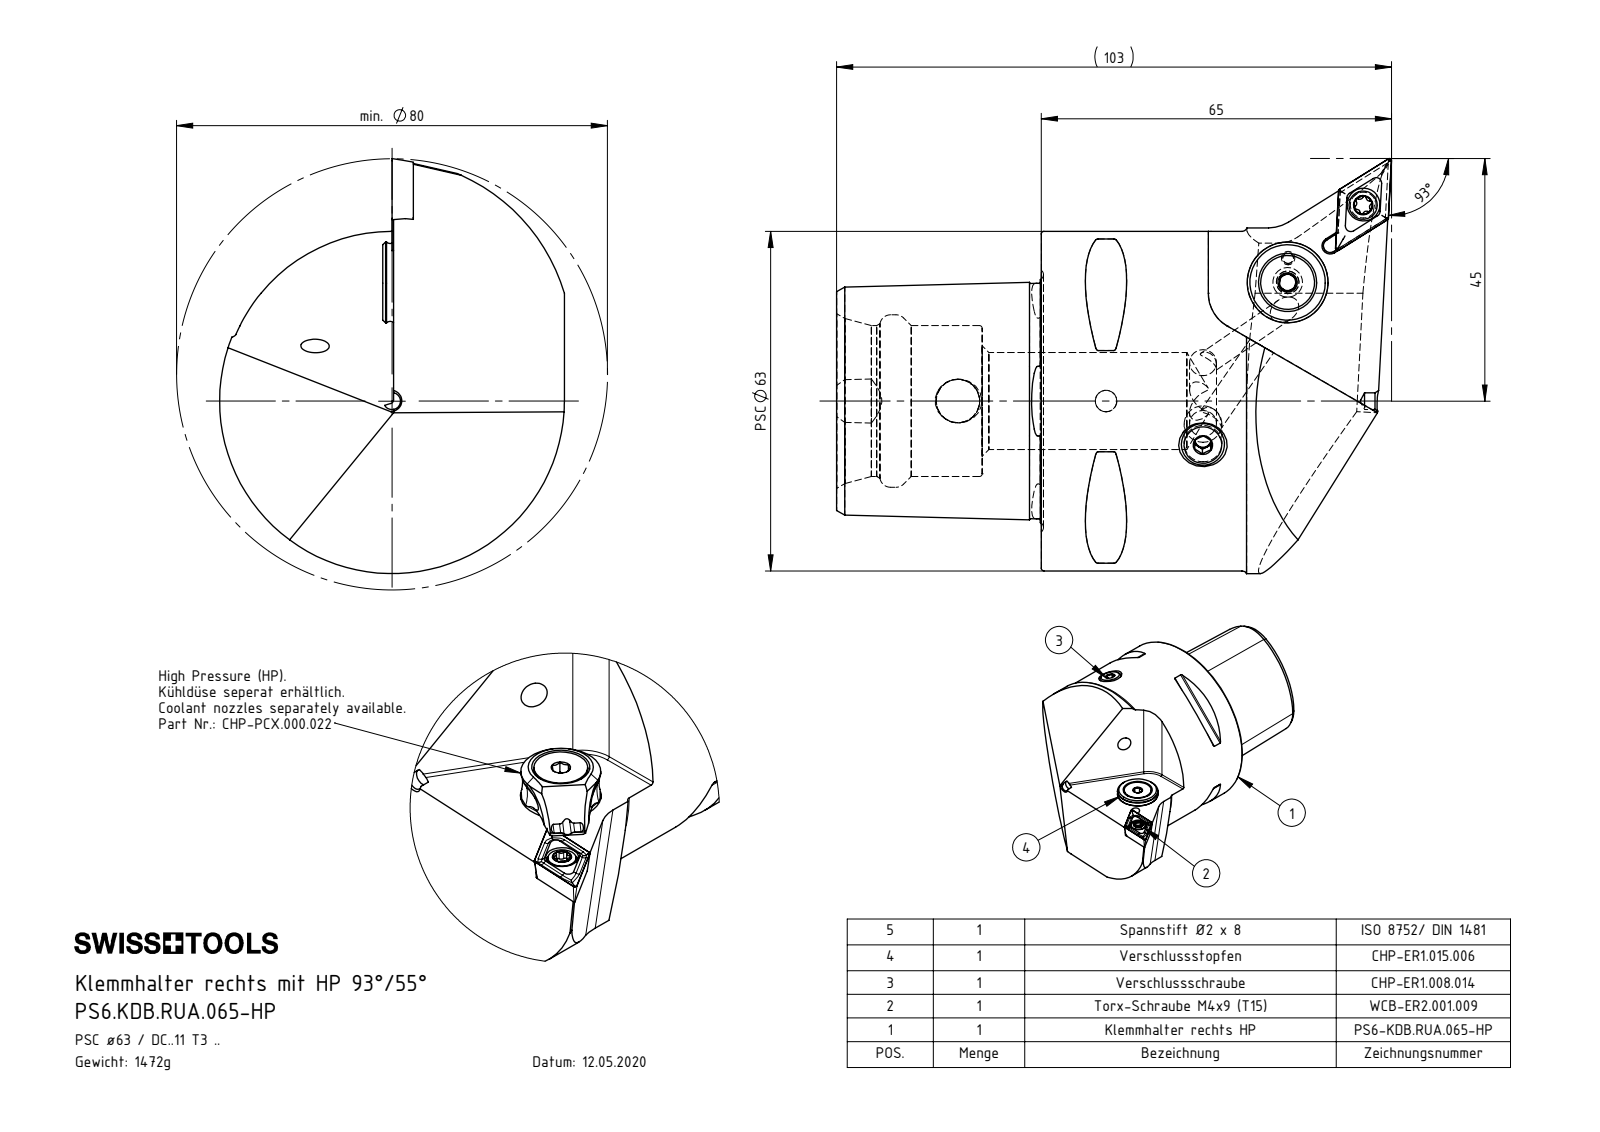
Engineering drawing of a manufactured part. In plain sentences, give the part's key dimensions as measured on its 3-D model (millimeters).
The part is named "DCMT11T304; PS6-KDB.RUA.065-HP_A; DIN 3771 - 13x1; DIN 7991 - M5x15 (+6 more)". Its 3-D file was written by "SolidWorks 2017 (AUTOMOTIVE_DESIGN)". It is 8 solids with 379 faces: 91 planar, 99 cylindrical and 189 other. Overall it measures 103 by 77.01 by 64 millimeters. Its volume is 187 205 cubic millimeters and its surface area 32 192 square millimeters. Round holes: 2 of diameter 4.2, 2 of diameter 5, 1 of diameter 1.2, 1 of diameter 2, 1 of diameter 2.5, 1 of diameter 3, 1 of diameter 3.3, 1 of diameter 4, 1 of diameter 4.4, 1 of diameter 5.2, 1 of diameter 6.1, 1 of diameter 7. Round bosses or shafts: 1 of diameter 63, 1 of diameter 15, 1 of diameter 13.4, 1 of diameter 10, 1 of diameter 8, 1 of diameter 5.5, 1 of diameter 5.25, 1 of diameter 5. Partial cylindrical surfaces (rounded edges, fillets, slot ends): 10 of radius 0.5, 6 of radius 0.34, 6 of radius 0.59, 2 of radius 7, 1 of radius 1.25, 1 of radius 1.57, 1 of radius 6, 1 of radius 32. The main face-to-face distances are 38, 31.7, 24.88, 27.2, 4.5, 27, 11, 69, 42, 31. The hole center spacings are 4.5, 17.07, 17.18, 20.05, 20.17, 27.5, 40.27, 42.95.
